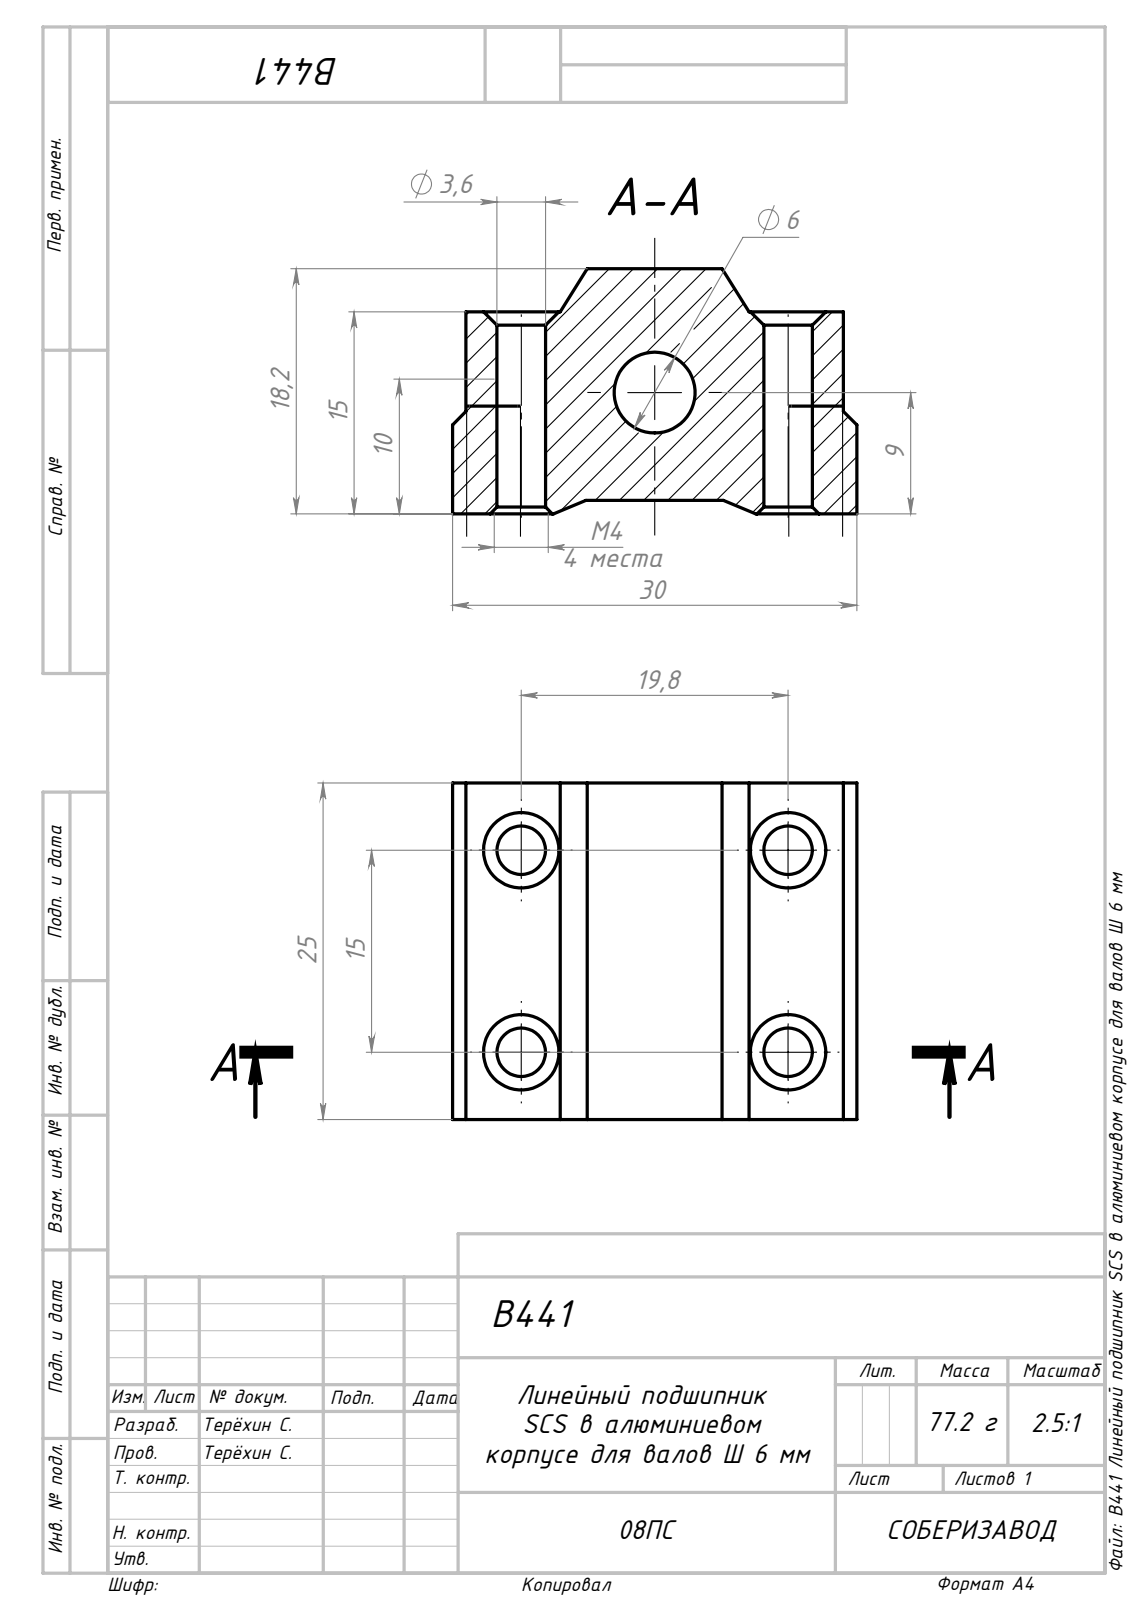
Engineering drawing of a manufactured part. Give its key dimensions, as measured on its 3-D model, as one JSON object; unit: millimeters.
{"part_name": "B441 Линейный подшипник SCS в алюминиевом корпусе для валов Ø 6 мм_00; Сборка1", "step_written_by": "SolidWorks 2024 (AUTOMOTIVE_DESIGN)", "units": "millimeters", "bodies": {"solids": 1, "faces": 50, "planar": 20, "cylindrical": 14, "other": 16}, "overall_size": [30, 25, 18.2], "volume_mm3": 9844, "surface_area_mm2": 4286, "round_holes": [[3.6, 4], [6, 1], [12, 1]], "face_to_face_distances": [1, 25, 29, 15, 14, 18.2, 17.2, 3.2, 28, 1.8], "hole_center_spacings": [15, 19.8, 24.84]}
